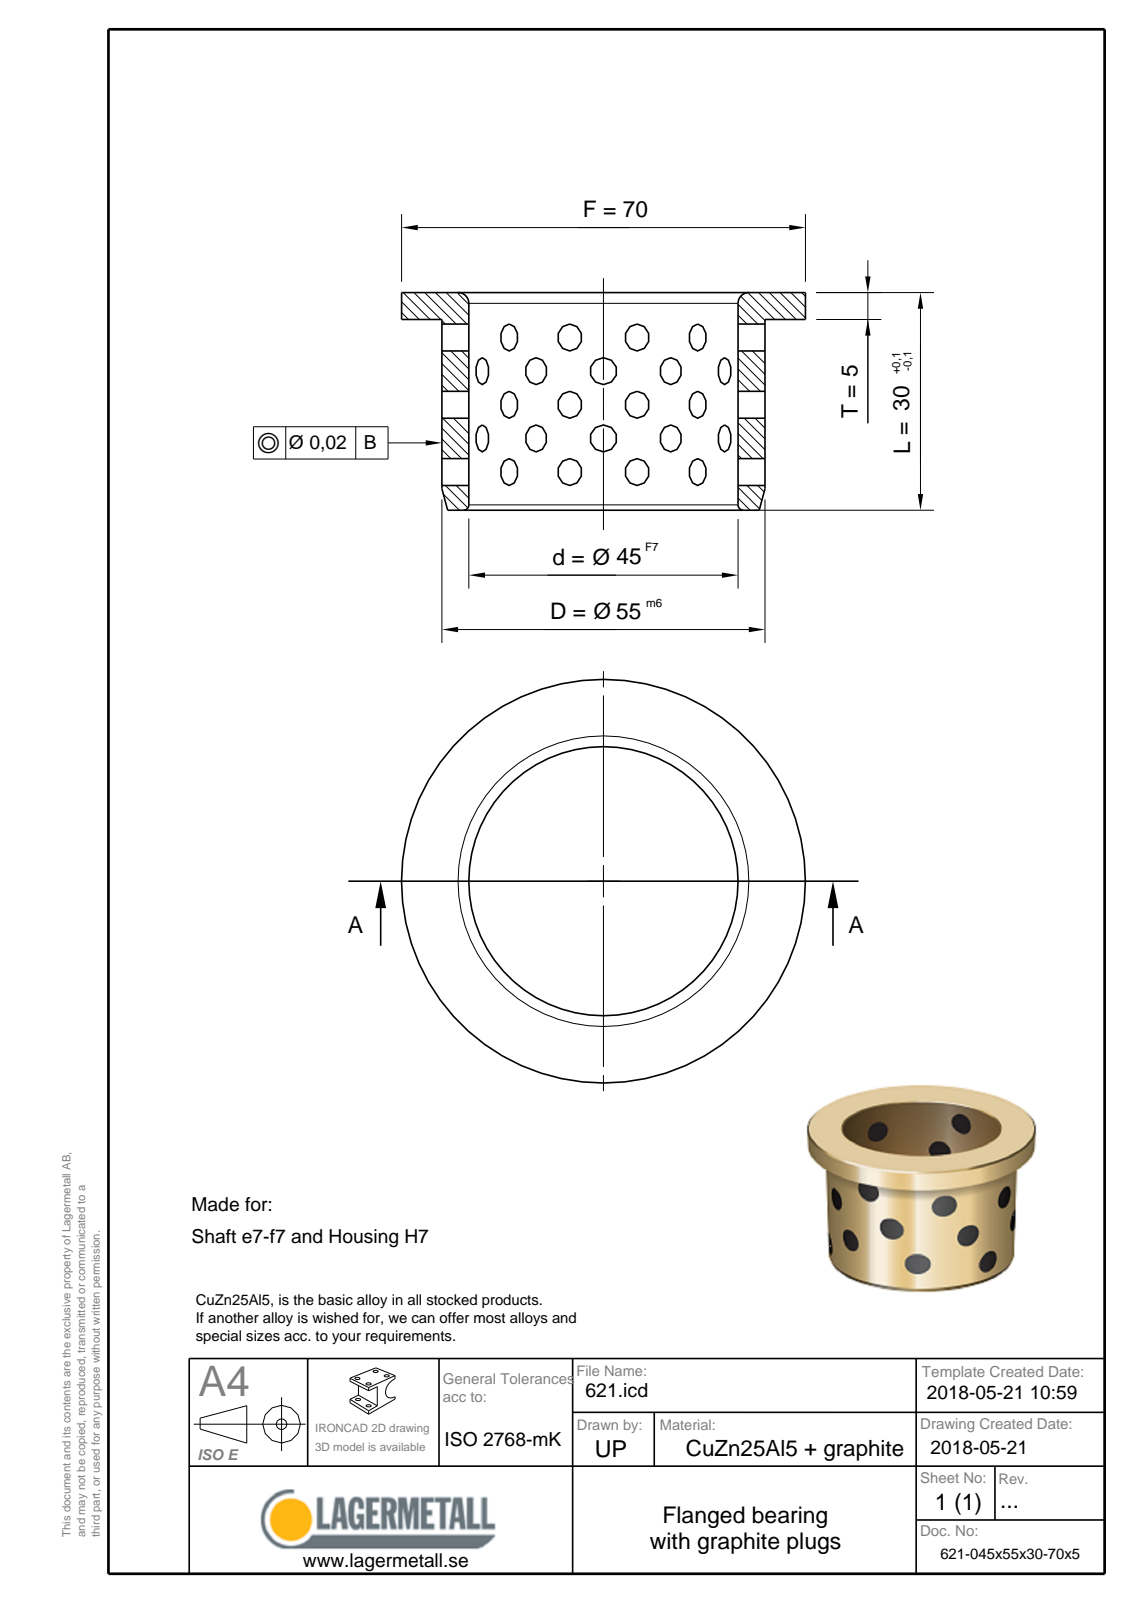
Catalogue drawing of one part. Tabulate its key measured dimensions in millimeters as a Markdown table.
| quantity | value |
| --- | --- |
| part name | 621-045x55x30-70x5 |
| STEP written by | Spatial InterOp 3D (CONFIG_CONTROL_DESIGN) |
| units | millimeters |
| bodies | 1 solid, 9 faces (3 planar, 3 cylindrical, 3 other) |
| overall size | 70 × 70 × 30 |
| volume | 30 473 mm³ |
| surface area | 13 812 mm² |
| round holes (diameter × count) | 45 × 1 |
| round bosses / shafts (diameter × count) | 70 × 1, 55 × 1 |
| main face-to-face distances | 5, 25, 30 |
